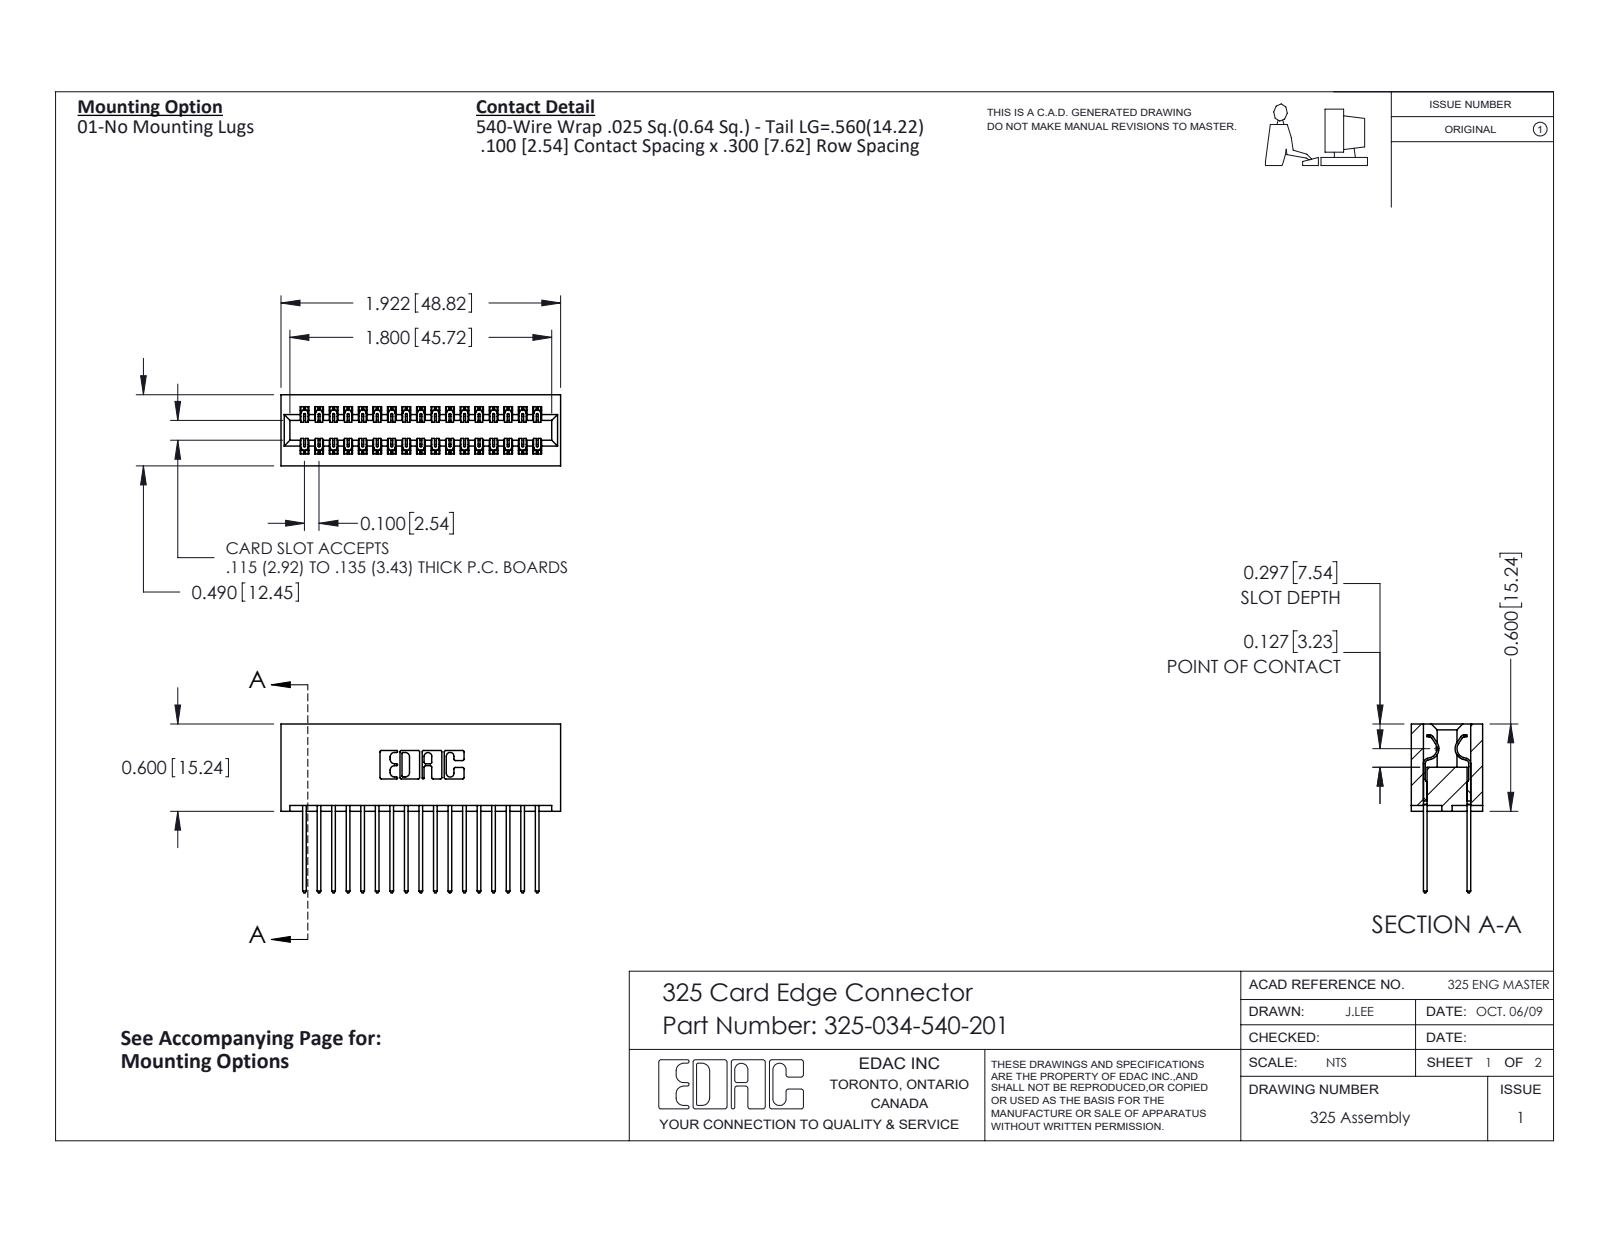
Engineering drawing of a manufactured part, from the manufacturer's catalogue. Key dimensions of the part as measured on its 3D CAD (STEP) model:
Part name (STEP PRODUCT): 325-292-001_325-293-140; 325-034-540-201; 325 Part_Lugless
STEP written by: SolidWorks 2016 (CONFIG_CONTROL_DESIGN)
Units: inches
Bodies: 35 solids, 1874 faces (1290 planar, 584 cylindrical, 0 other)
Overall size (bounding box): 1.922 × 1.16 × 0.49
Volume: 0.416 in³ · Surface area: 13.84 in²
Partial cylindrical surfaces — rounded edges, fillets, slot ends (radius × count): R0.006 ×51, R0.01 ×34, R0.01 ×22, R0.007 ×6, R0.031 ×6, R0.026 ×3, R0.014 ×2, R0.022 ×2
Main face-to-face distances: 0.083, 0.407, 0.3, 0.107, 0.383, 0.025, 0.325, 0.49, 0.2, 0.56
